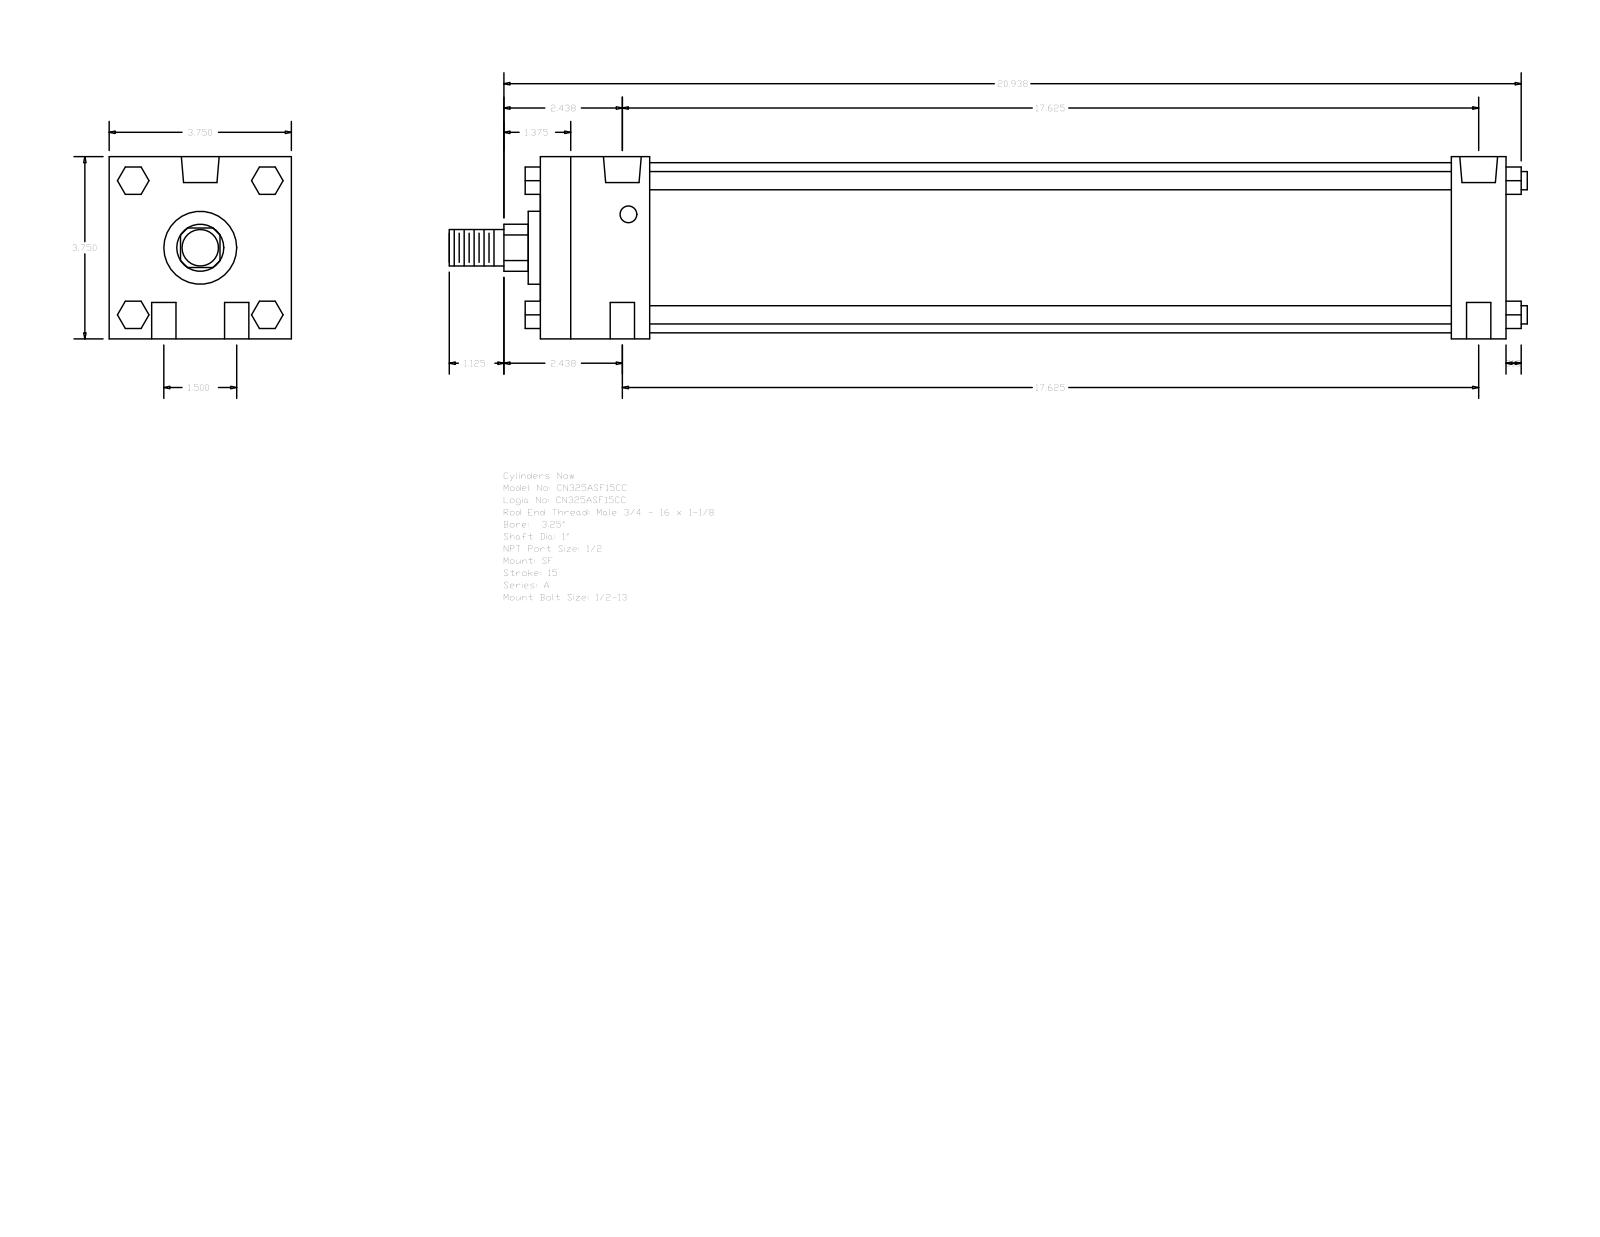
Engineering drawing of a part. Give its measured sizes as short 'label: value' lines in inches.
name: A_SF__0325_1
written by: GSSL Pune (CONFIG_CONTROL_DESIGN)
unit: in
bodies: 0 solids, 124 faces (94 planar, 30 cylindrical, 0 other)
size: 22.187 × 3.75 × 3.75
holes: 4× ⌀0.5, 2× ⌀0.344, 2× ⌀0.778
bosses: 4× ⌀0.375, 1× ⌀3.5, 1× ⌀1.5, 1× ⌀1, 1× ⌀0.75
rounds: 1× R0.484
face distances: 3.75, 19.875, 18.75, 1.125, 2.25, 16.5, 17.625, 0.562, 1.38, 2.39
hole spacings: 0.75, 17.641, 17.625, 1.5, 17.689, 17.375
